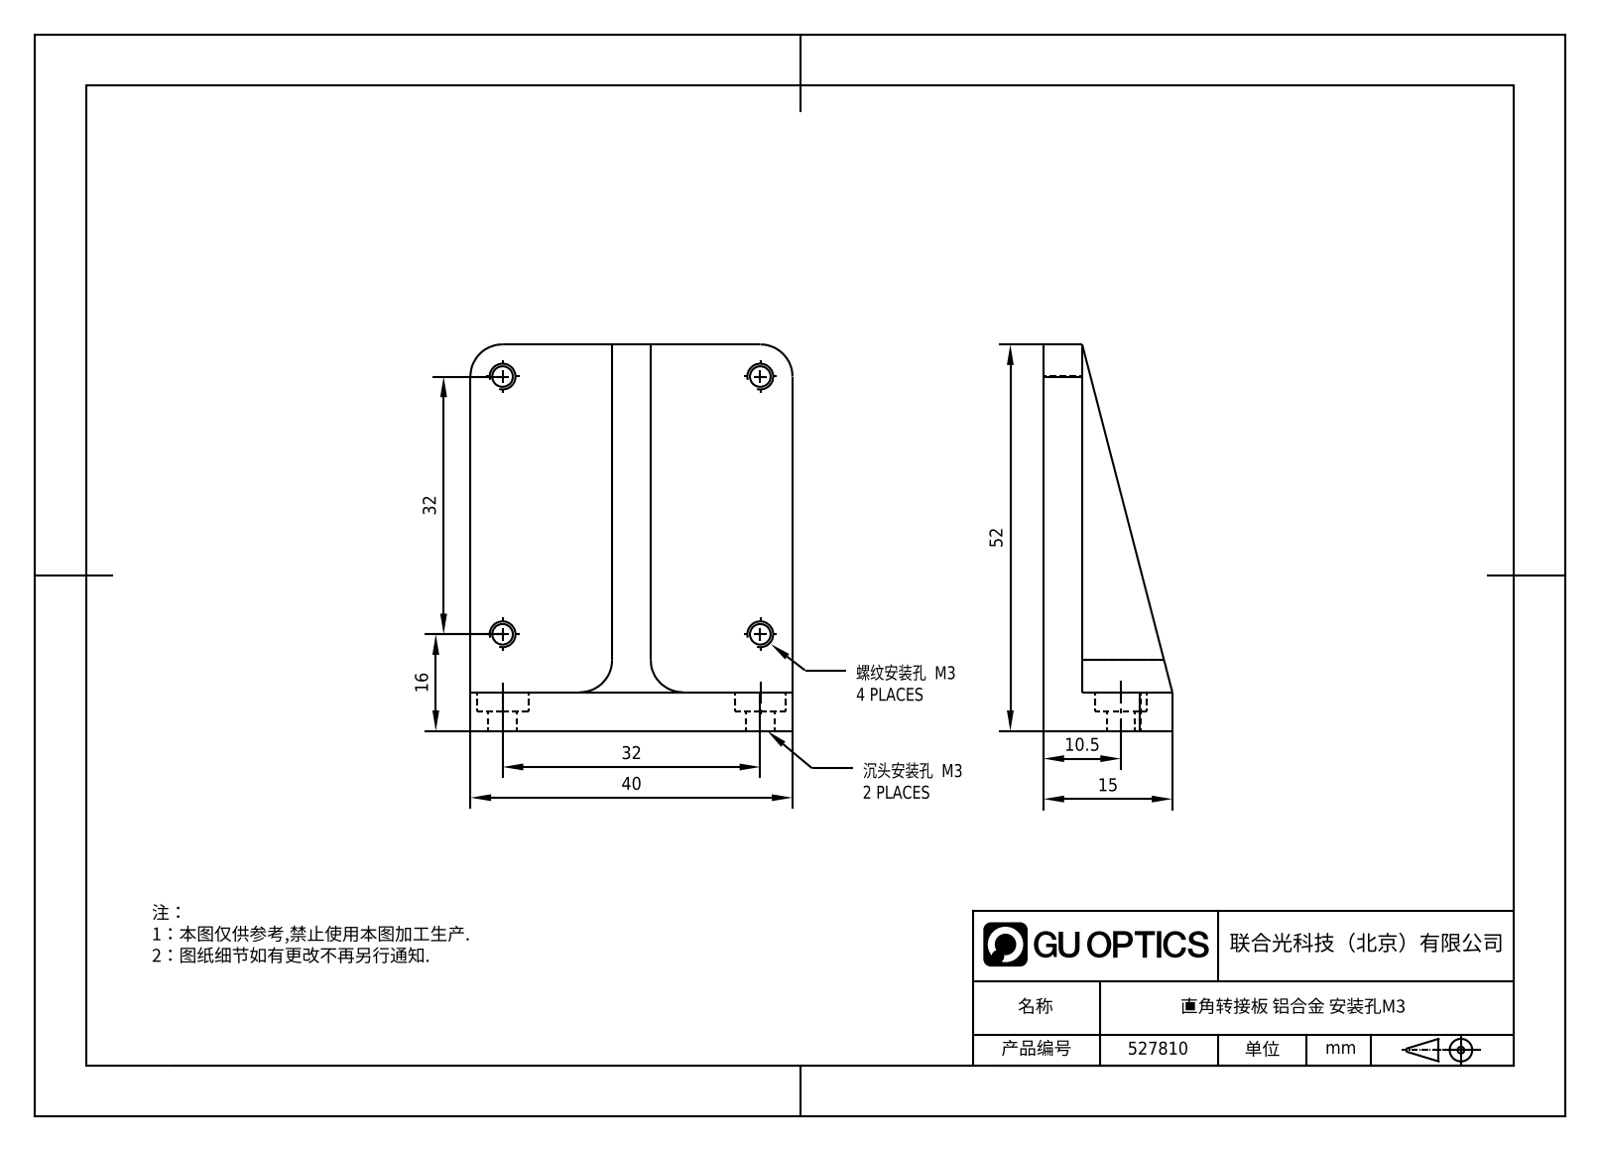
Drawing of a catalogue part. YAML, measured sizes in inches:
part_name: "1.6.9.2_ZSJ-Z040_40mm直角转接板，带M3螺孔和M3沉头孔"
step_written_by: "SolidWorks 2021 (CONFIG_CONTROL_DESIGN)"
units: inches
bodies: {solids: 1, faces: 37, planar: 15, cylindrical: 22, other: 0}
overall_size: [2.047, 1.575, 0.591]
volume: 0.811
surface_area: 10.13
round_holes:
  - {diameter: 0.098, count: 4}
  - {diameter: 0.138, count: 2}
  - {diameter: 0.236, count: 2}
partial_cylinders:
  - {radius: 0.157, count: 6}
face_to_face_distances: [0.197, 0.689, 0.886, 1.575, 0.591, 0.394, 2.047, 1.85, 0.098, 1.949]
hole_center_spacings: [1.26, 1.781]
